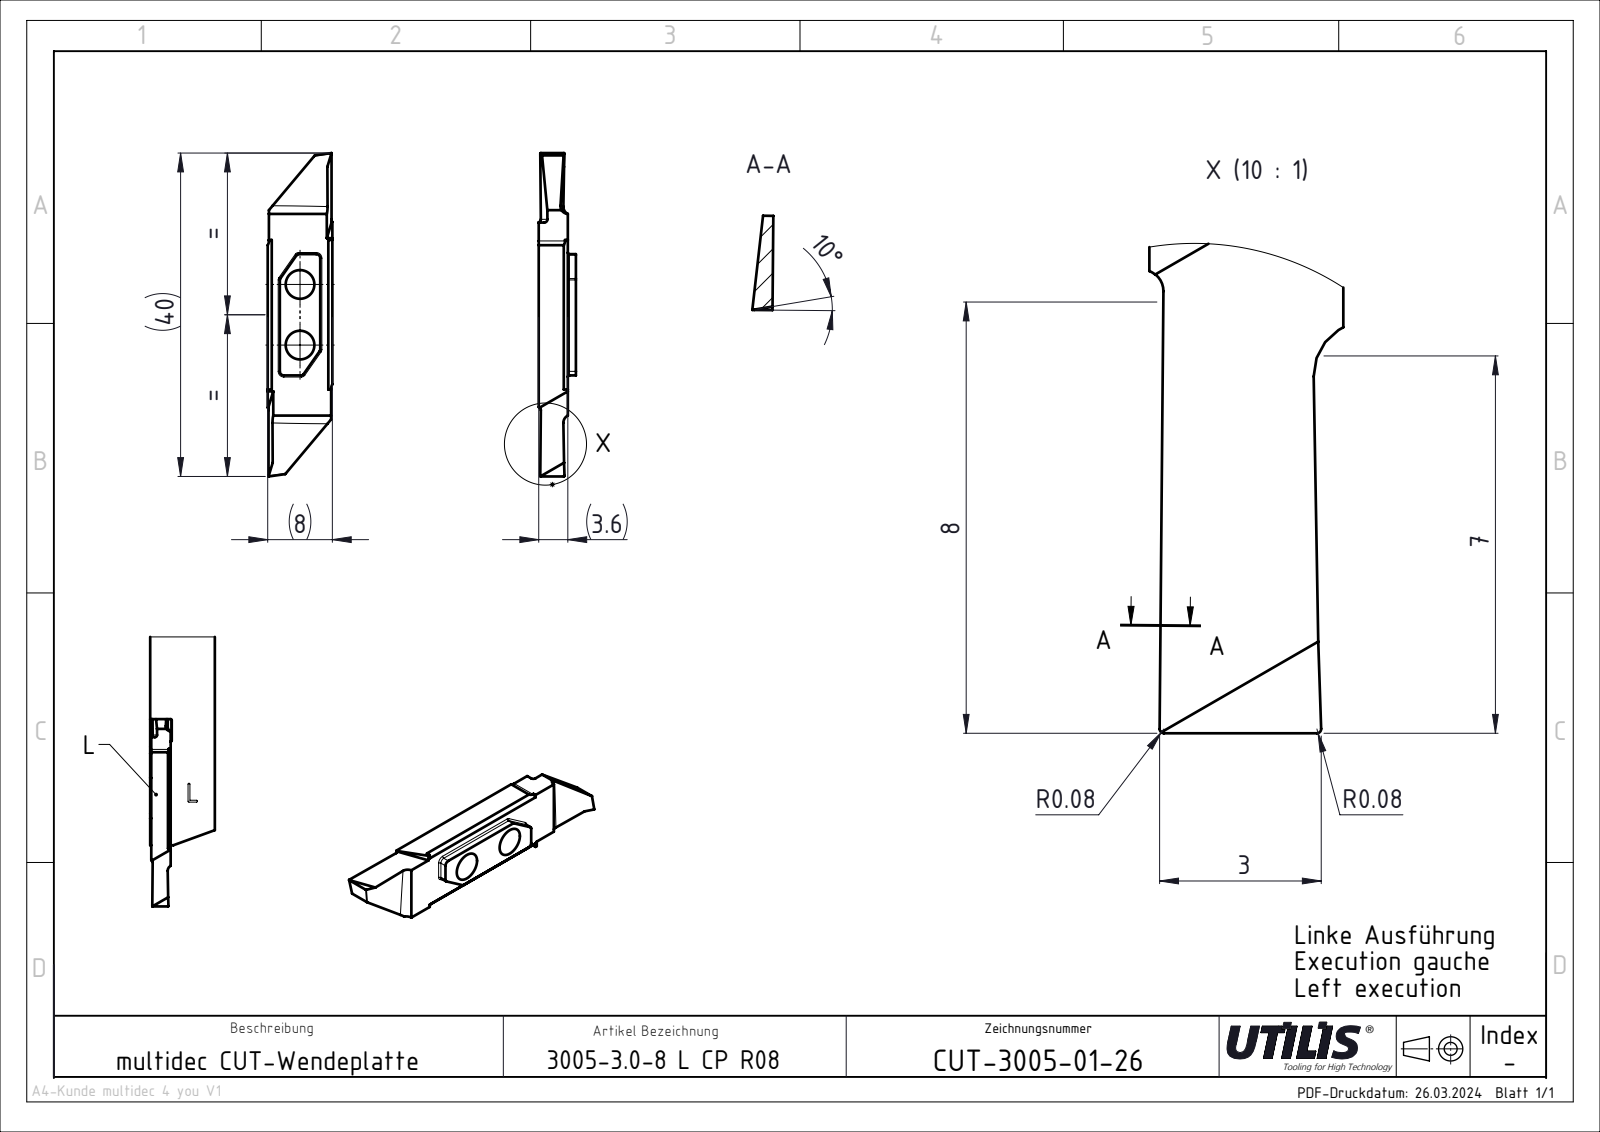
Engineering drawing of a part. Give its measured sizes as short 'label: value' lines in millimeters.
name: CUT-3005 CP; ASME Y14.5
written by: SolidWorks 2023 SP4 || FormatWorks Professional (AP242_MANAGED_MODEL_BASED_3D_ENGINEERING_MIM_LF)
unit: mm
bodies: 1 solid, 34 faces (20 planar, 14 cylindrical, 0 other)
size: 40 × 8 × 3.6
volume: 857 mm³; area: 875 mm²
holes: 2× ⌀3.55
rounds: 4× R1, 2× R0.4
face distances: 3.6, 8, 22.54, 7.85, 7.7, 40, 10.75, 29.25, 18.5
hole spacings: 7.49
